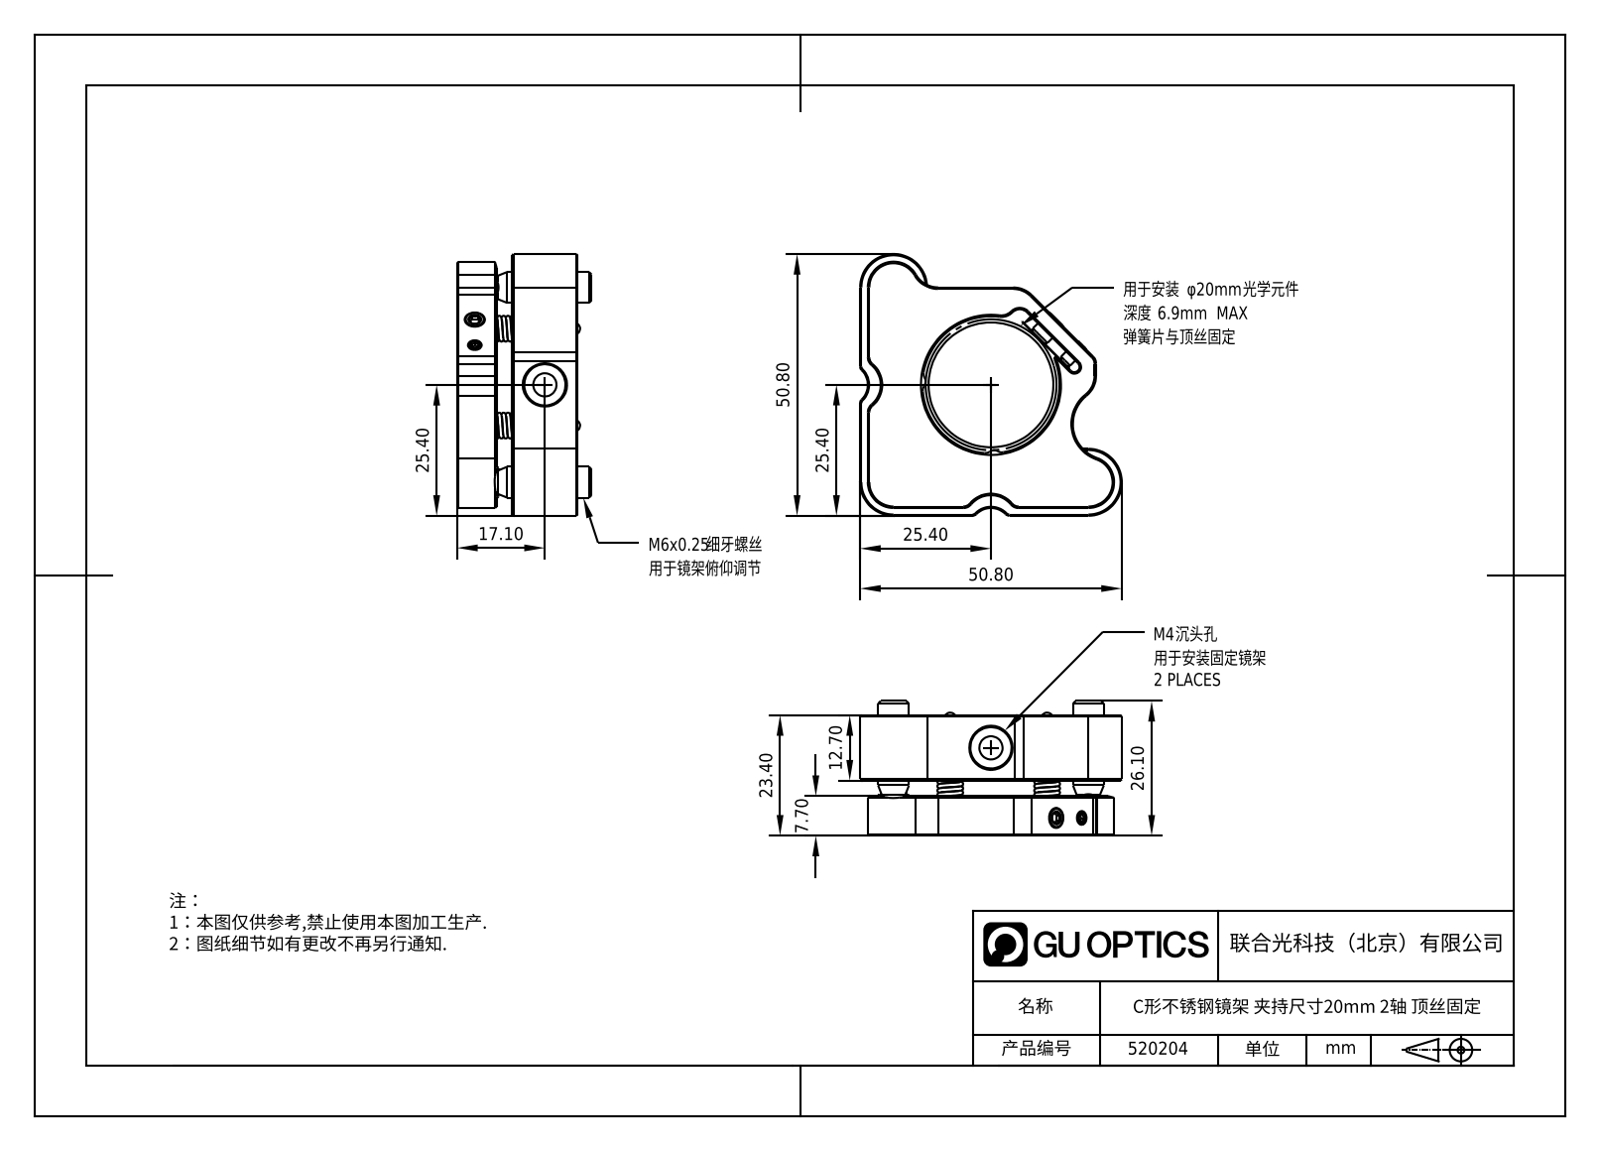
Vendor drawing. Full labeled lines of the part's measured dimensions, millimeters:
Part name (STEP PRODUCT): DXS-0625标准型六角调节器 _3.2.2.15.1-DXS-0625-20; 30.5.87-93，LPJ2.5，M2.5不锈钢平头紧定螺丝_30.5.89-PJ2.5*5; 不锈钢方形压片_32.6.12-QY-1305-0.2; 36.1，440c不锈钢滚珠_36.1.6_GZ-B4 (+5 more)
STEP written by: SolidWorks 2021 (CONFIG_CONTROL_DESIGN)
Units: millimetres
Bodies: 19 solids, 556 faces (185 planar, 151 cylindrical, 220 other)
Overall size (bounding box): 50.8 × 50.8 × 26.66
Volume: 21 417 mm³ · Surface area: 13 971 mm²
Round holes (diameter × count): ⌀2.5 ×4, ⌀6 ×4, ⌀2 ×2, ⌀3.99 ×2, ⌀4.5 ×2, ⌀5.75 ×2, ⌀6.35 ×2, ⌀8 ×2, ⌀1.2 ×1, ⌀2.05 ×1, ⌀3.3 ×1, ⌀18.8 ×1
Round bosses / shafts (diameter × count): ⌀4 ×7, ⌀6 ×2, ⌀3 ×1, ⌀2.5 ×1, ⌀2 ×1
Partial cylindrical surfaces — rounded edges, fillets, slot ends (radius × count): R5 ×10, R1 ×9, R1.05 ×8, R1.5 ×6, R2 ×6, R6.5 ×3, R4 ×2, R3 ×1
Main face-to-face distances: 7.7, 3.53, 11.23, 12.7, 16.23, 23.93, 1.5, 11.5, 13, 0.5
Hole centre spacings: 18.8, 26.73, 5, 8, 11, 14.38, 16.14, 17.81
